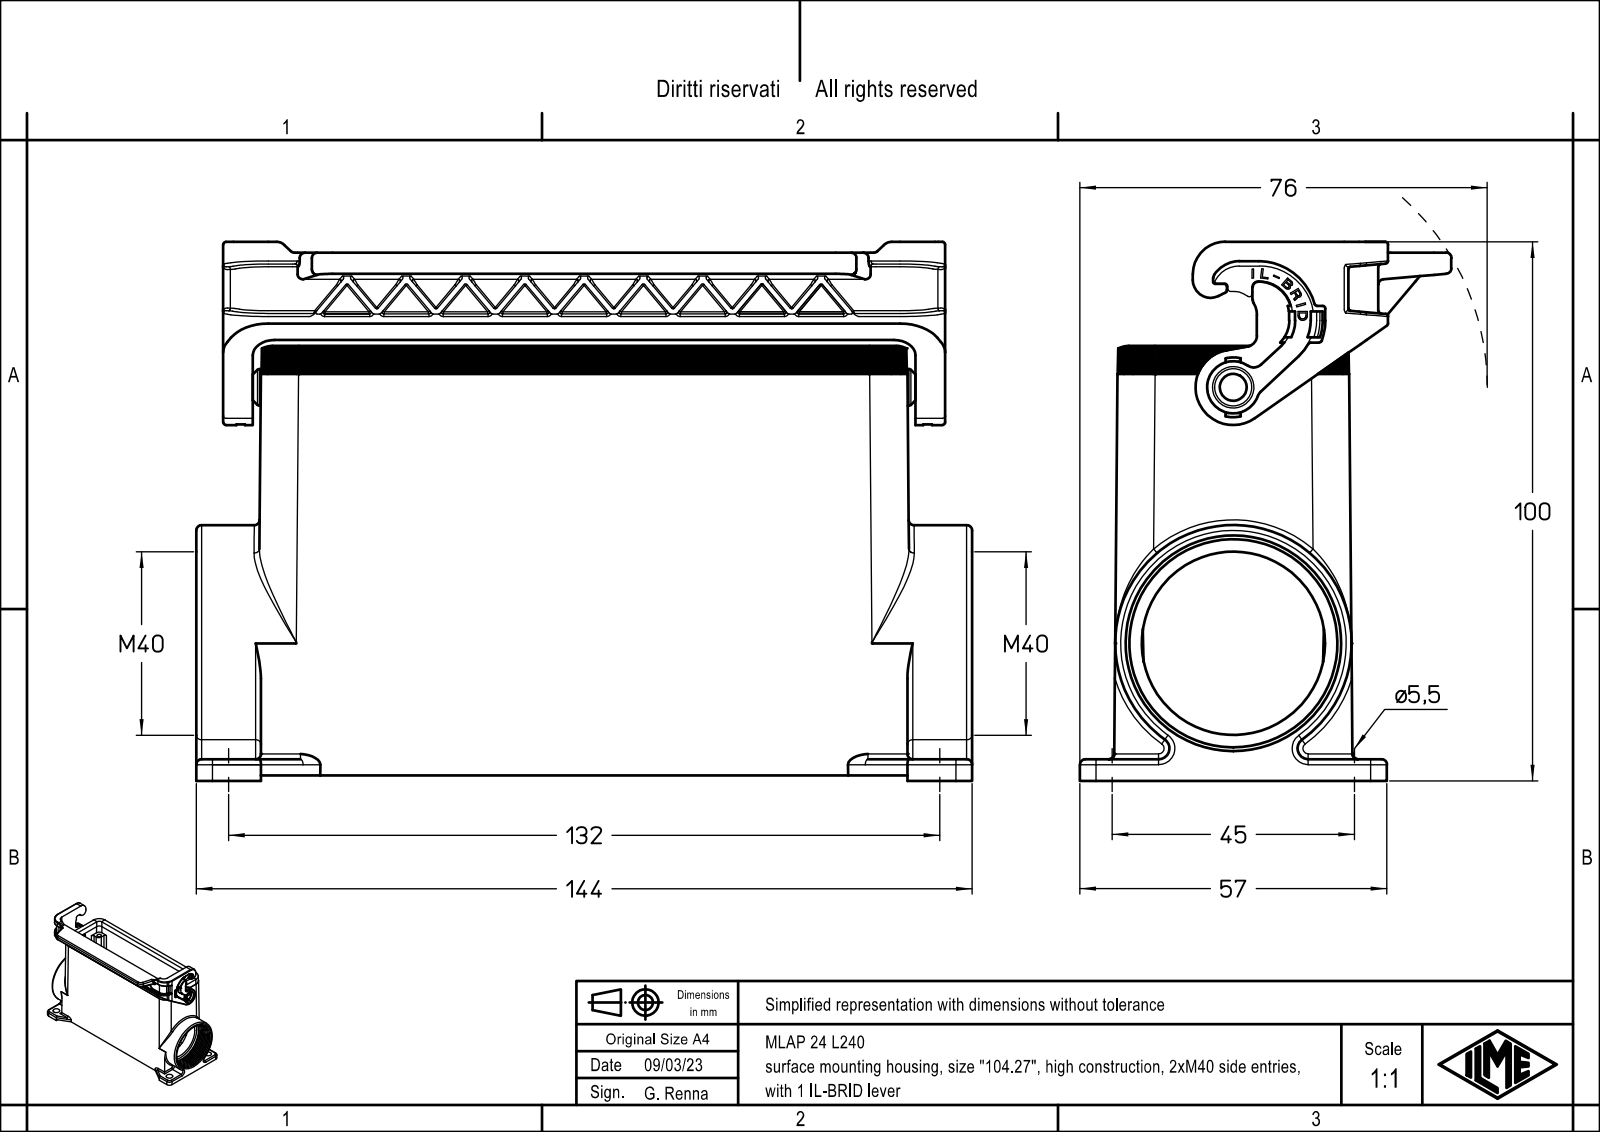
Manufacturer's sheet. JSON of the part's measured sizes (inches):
{"part_name": "MLAP 24 L240", "step_written_by": "Creo Elements/Direct Modeling 20.1B 02-Apr-2019 (C) Parametric Technology GmbH (AUTOMOTIVE_DESIGN)", "units": "inches", "bodies": {"solids": 1, "faces": 1129, "planar": 659, "cylindrical": 298, "other": 172}, "overall_size": [5.669, 3.937, 2.715], "volume_in3": 9.314, "surface_area_in2": 126.9, "round_holes": [[0.118, 4], [0.138, 4], [0.217, 4], [0.128, 1], [0.213, 1], [0.303, 1], [1.339, 1], [1.52, 1]], "round_bosses_or_shafts": [[1.727, 1], [0.272, 1], [0.268, 1], [0.205, 1], [0.126, 1]], "partial_cylinders_radius": [[0.004, 27], [0.039, 16], [0.118, 16], [0.008, 15], [0.02, 11], [0.079, 11], [0.276, 10], [0.059, 9]], "face_to_face_distances": [0.118, 0.157, 3.819, 3.701, 0.217, 0.039, 0.276, 4.843, 1.531, 0.197], "hole_center_spacings": [0.655, 1.521, 4.659, 4.857, 1.063, 1.772, 4.094, 4.23]}
